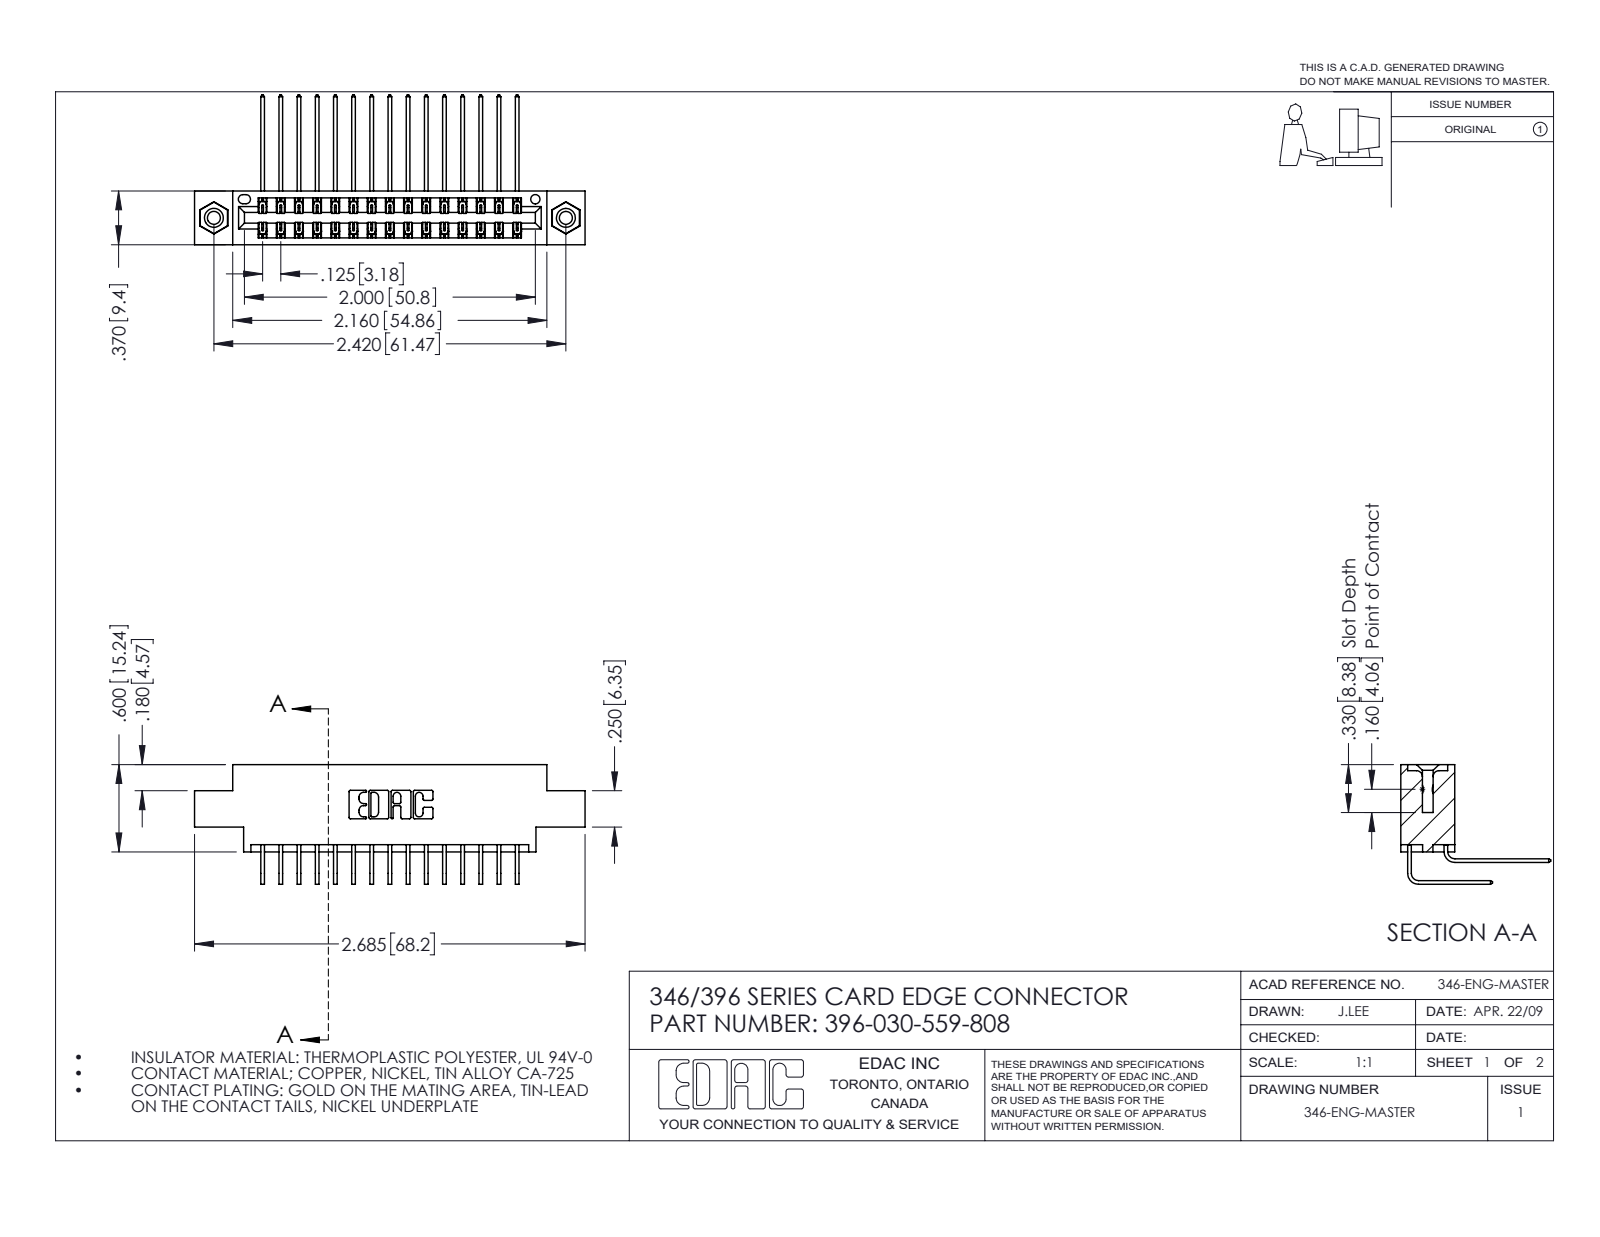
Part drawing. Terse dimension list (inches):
name: 345-292-001_558 559 Tail - 1; 345-292-001_559 Tail - 2; 345-250-001_345-250-003-102; 396-030-559-808 (+1 more)
written by: SolidWorks 2016 (CONFIG_CONTROL_DESIGN)
unit: in
bodies: 33 solids, 1806 faces (1222 planar, 568 cylindrical, 16 other)
size: 2.685 × 1.03 × 0.823
volume: 0.394 in³; area: 14.69 in²
holes: 2× ⌀0.089, 2× ⌀0.125, 2× ⌀0.156, 1× ⌀0.064
bosses: 2× ⌀0.155
rounds: 45× R0.006, 22× R0.01, 6× R0.007, 6× R0.031, 3× R0.026, 2× R0.014, 2× R0.022, 2× R0.024
face distances: 0.048, 0.322, 0.37, 0.25, 0.025, 0.072, 0.298, 0.275, 0.222, 0.148
hole spacings: 0.246, 2.213, 2.42
